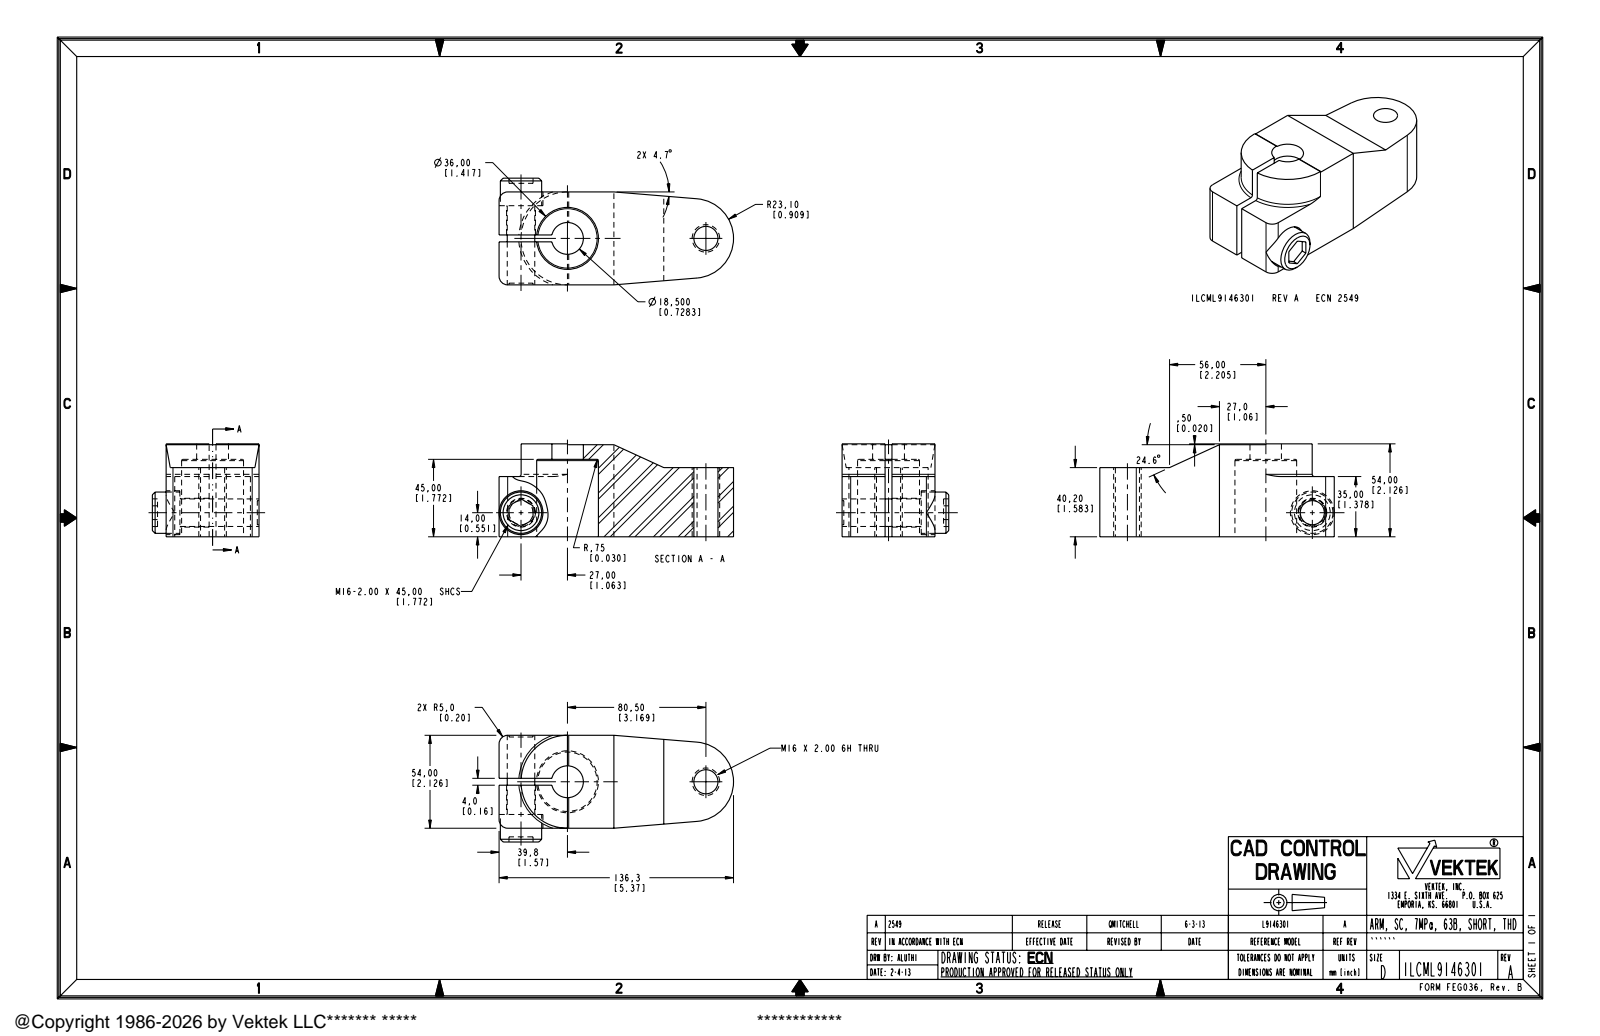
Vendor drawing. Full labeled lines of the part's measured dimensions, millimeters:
Part name (STEP PRODUCT): ILCML9146301
STEP written by: PRO/ENGINEER BY PARAMETRIC TECHNOLOGY CORPORATION, 2007460 (AUTOMOTIVE_DESIGN_CC2)
Units: millimetres
Bodies: 1 solid, 59 faces (28 planar, 26 cylindrical, 5 other)
Overall size (bounding box): 136.3 × 62 × 54
Volume: 256 581 mm³ · Surface area: 44 285 mm²
Round holes (diameter × count): ⌀14 ×2, ⌀16.75 ×1, ⌀18.5 ×1, ⌀25.5 ×1, ⌀36 ×1
Round bosses / shafts (diameter × count): ⌀16 ×2, ⌀24 ×1
Partial cylindrical surfaces — rounded edges, fillets, slot ends (radius × count): R5 ×2, R0.8 ×1, R23.1 ×1, R27 ×1
Main face-to-face distances: 54, 25, 29, 40.2, 53.5, 13.3, 13.8, 0.5, 35, 5.2
Hole centre spacings: 80.5
